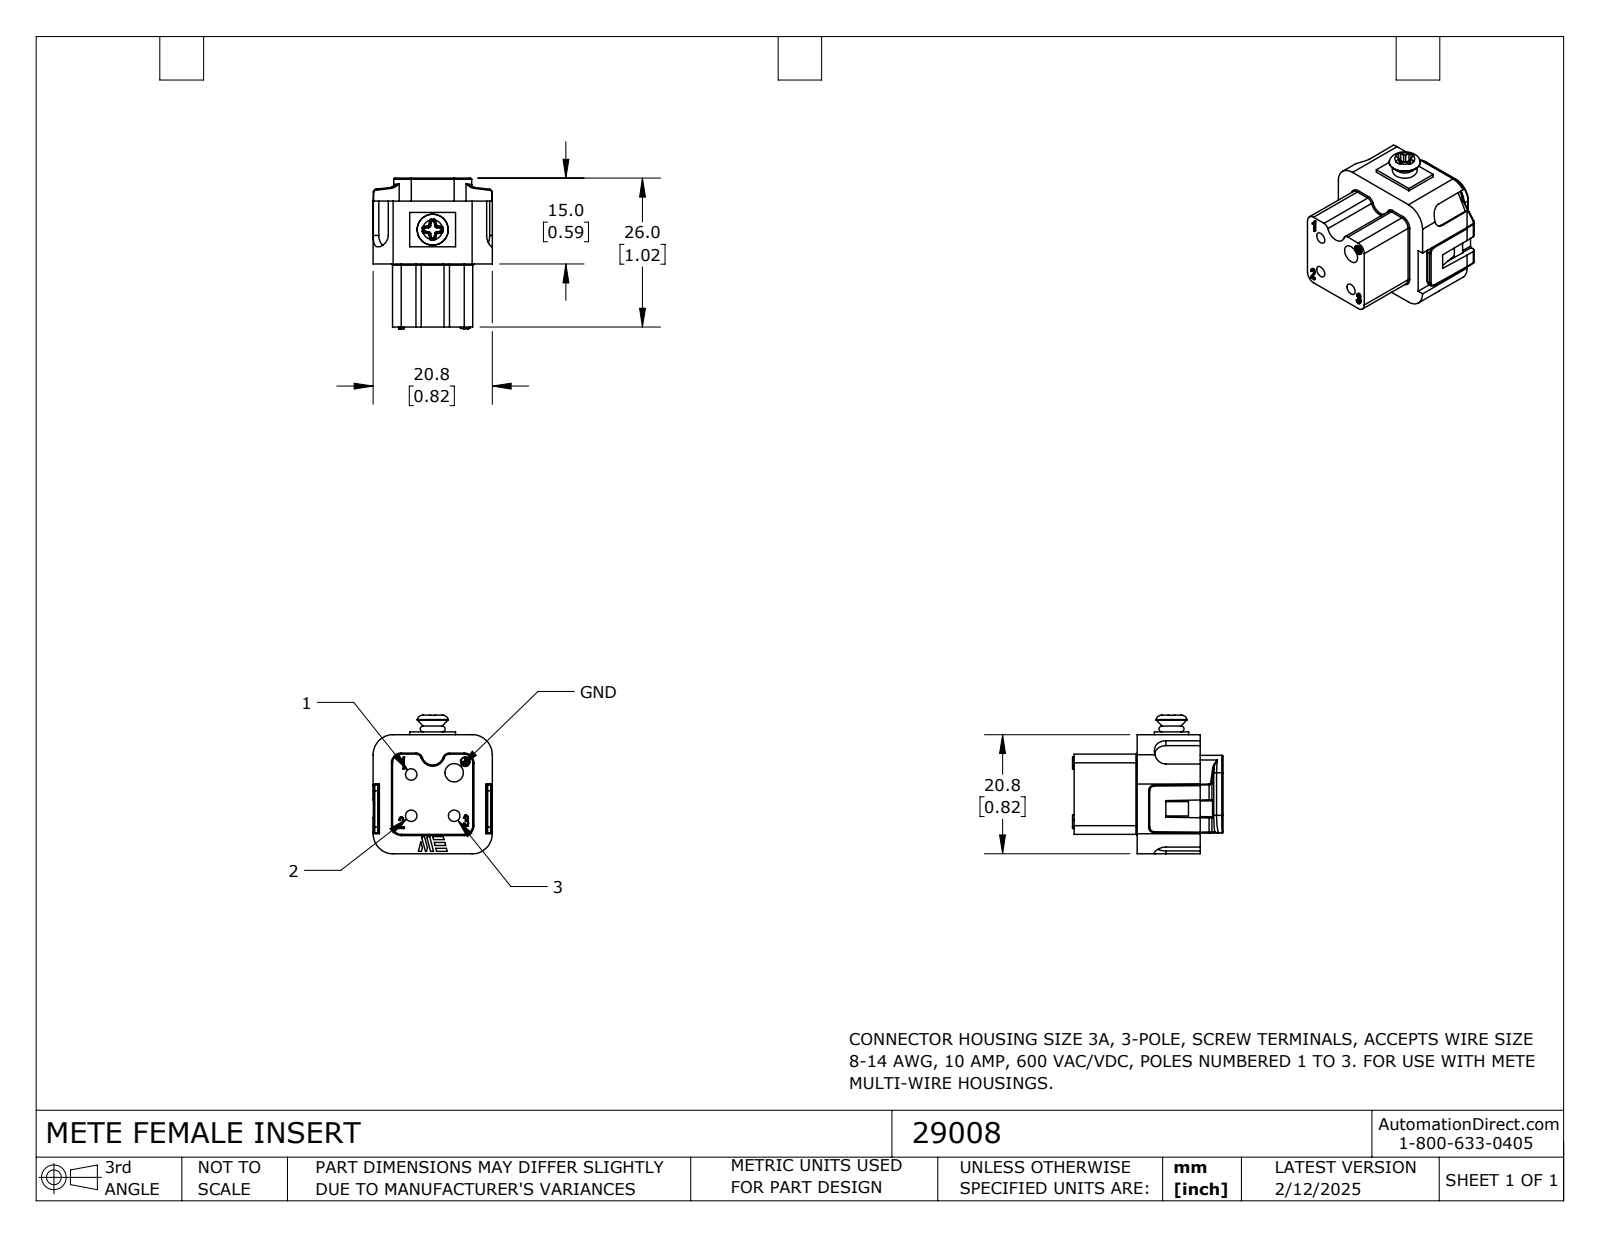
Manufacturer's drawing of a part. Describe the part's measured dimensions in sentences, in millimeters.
The part is named "29008". Its 3-D file was written by "SolidWorks 2024 (CONFIG_CONTROL_DESIGN)". It is 1 solid with 504 faces: 229 planar, 135 cylindrical and 140 other. Overall it measures 26.3 by 24.2 by 20.8 millimeters. Its volume is 7 030 cubic millimeters and its surface area 3 831 square millimeters. Round holes: 4 of diameter 3.3, 3 of diameter 2, 1 of diameter 1.5, 1 of diameter 3.2. Round bosses or shafts: 4 of diameter 2.9, 4 of diameter 2.4, 1 of diameter 1.7. Partial cylindrical surfaces (rounded edges, fillets, slot ends): 40 of radius 0.2, 12 of radius 0.1, 12 of radius 0.3, 4 of radius 0.5, 4 of radius 1.5, 4 of radius 2, 4 of radius 3, 4 of radius 3.5. The main face-to-face distances are 11, 3.4, 17.4, 22, 20.8, 4, 1, 14, 15, 1.1. The hole center spacings are 7.5, 2.7, 7.2, 7.5, 9.6, 9.7, 10.4, 10.6.
